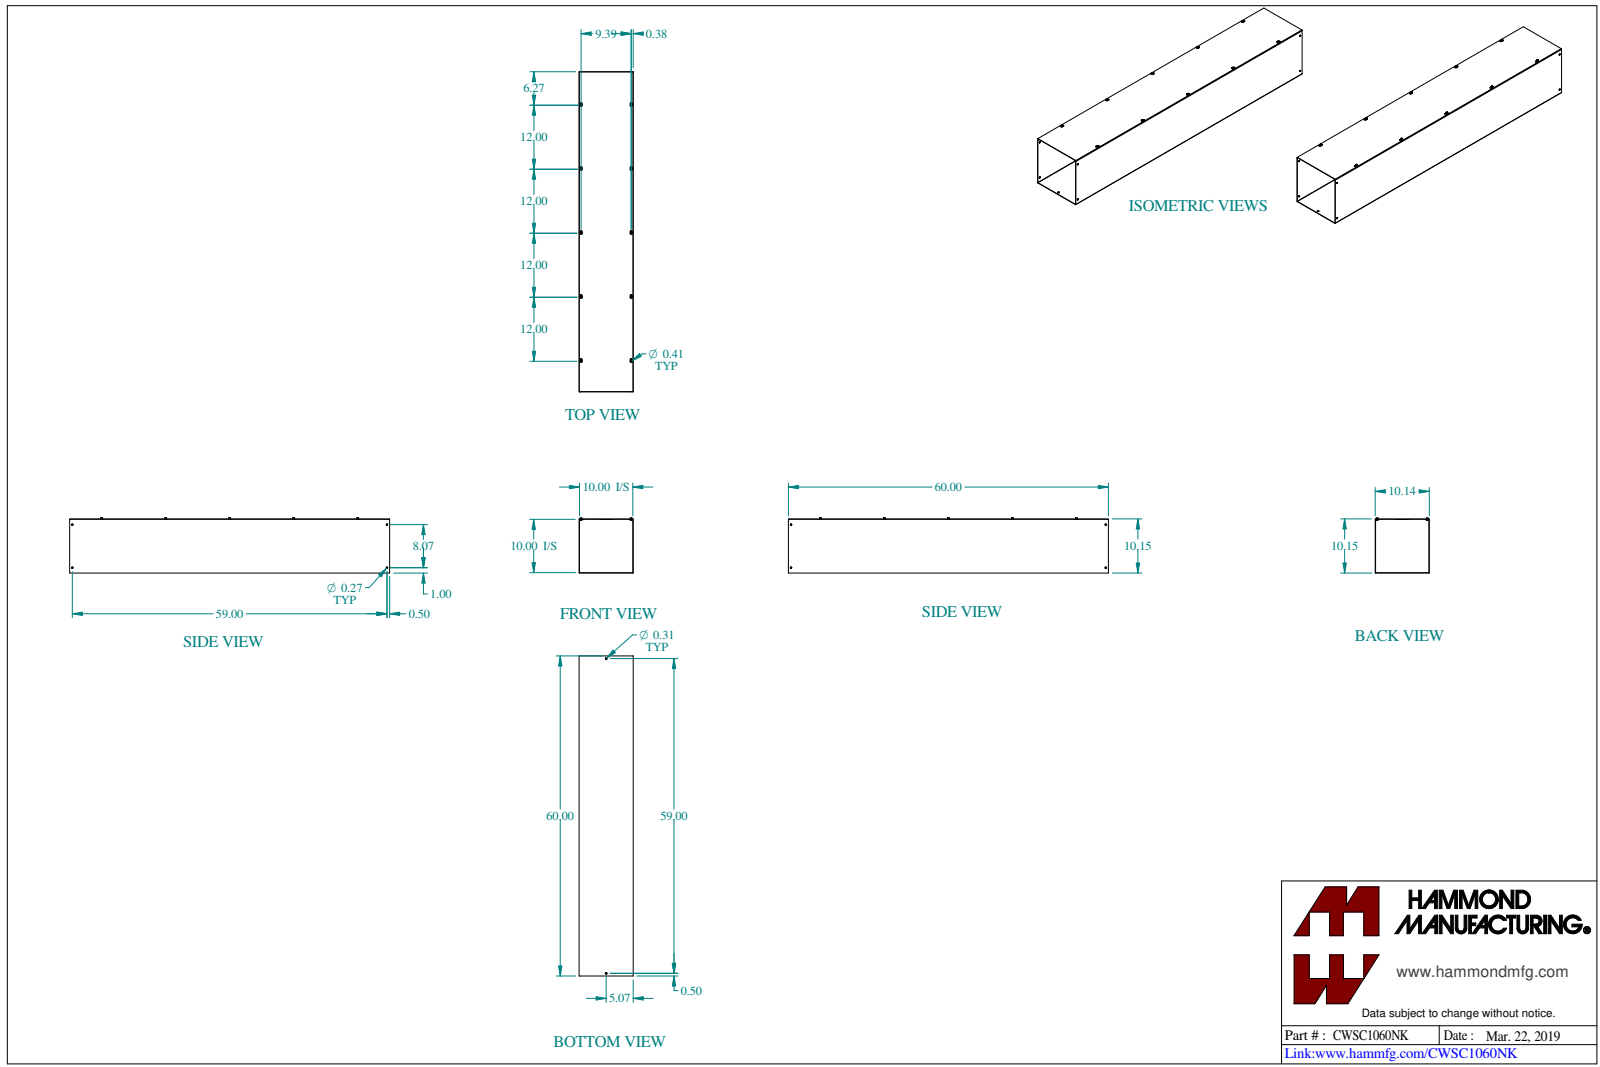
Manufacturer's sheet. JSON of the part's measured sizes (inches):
{"part_name": "CWSC1060NK", "step_written_by": "SolidWorks 2023 (CONFIG_CONTROL_DESIGN)", "units": "inches", "bodies": {"solids": 12, "faces": 366, "planar": 178, "cylindrical": 128, "other": 60}, "overall_size": [60, 10.325, 10.144], "volume_in3": 182.6, "surface_area_in2": 4997, "round_holes": [[0.177, 10], [0.266, 4], [0.313, 2]], "round_bosses_or_shafts": [[0.375, 10], [0.19, 10]], "partial_cylinders_radius": [[0.125, 10], [0.203, 10], [0.036, 4], [0.108, 4]], "face_to_face_distances": [0.072, 10.072, 10, 0.078, 10.15, 10.078, 10.144, 9.928, 0.15, 0.031], "hole_center_spacings": [12, 15.239, 24, 25.773, 9.394, 7.233, 18.119, 29.872]}
